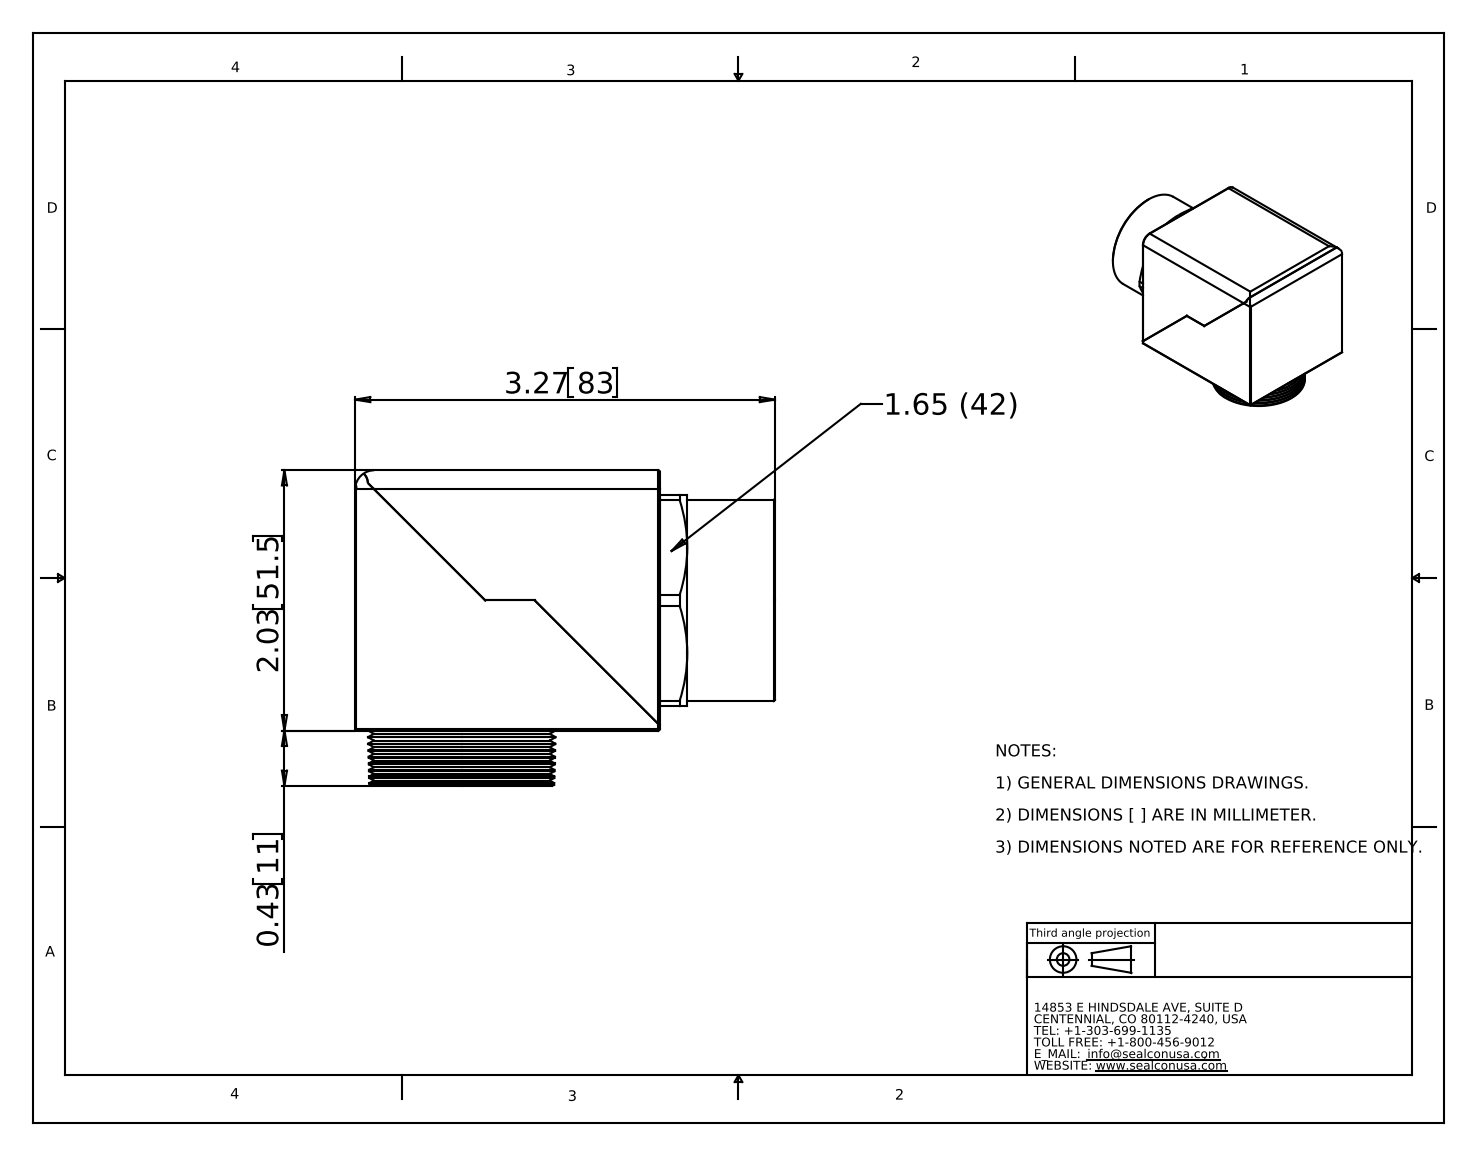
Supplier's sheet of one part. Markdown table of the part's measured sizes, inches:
| quantity | value |
| --- | --- |
| part name | EM29AA-BK |
| STEP written by | SolidWorks 2007 (AUTOMOTIVE_DESIGN) |
| units | inches |
| bodies | 2 solids, 134 faces (31 planar, 34 cylindrical, 69 other) |
| overall size | 3.27 × 2.46 × 2.03 |
| volume | 9.445 in³ |
| surface area | 57.14 in² |
| round holes (diameter × count) | 0.803 × 2, 1.47 × 1 |
| round bosses / shafts (diameter × count) | 1.567 × 1 |
| partial cylindrical surfaces (radius × count) | 0.01 × 7, 0.147 × 3, 0.098 × 1, 0.928 × 1 |
| main face-to-face distances | 2.03, 0.27, 2.373, 1.015, 0.215, 2.588, 0.43, 2.46, 1.445, 0.19 |
